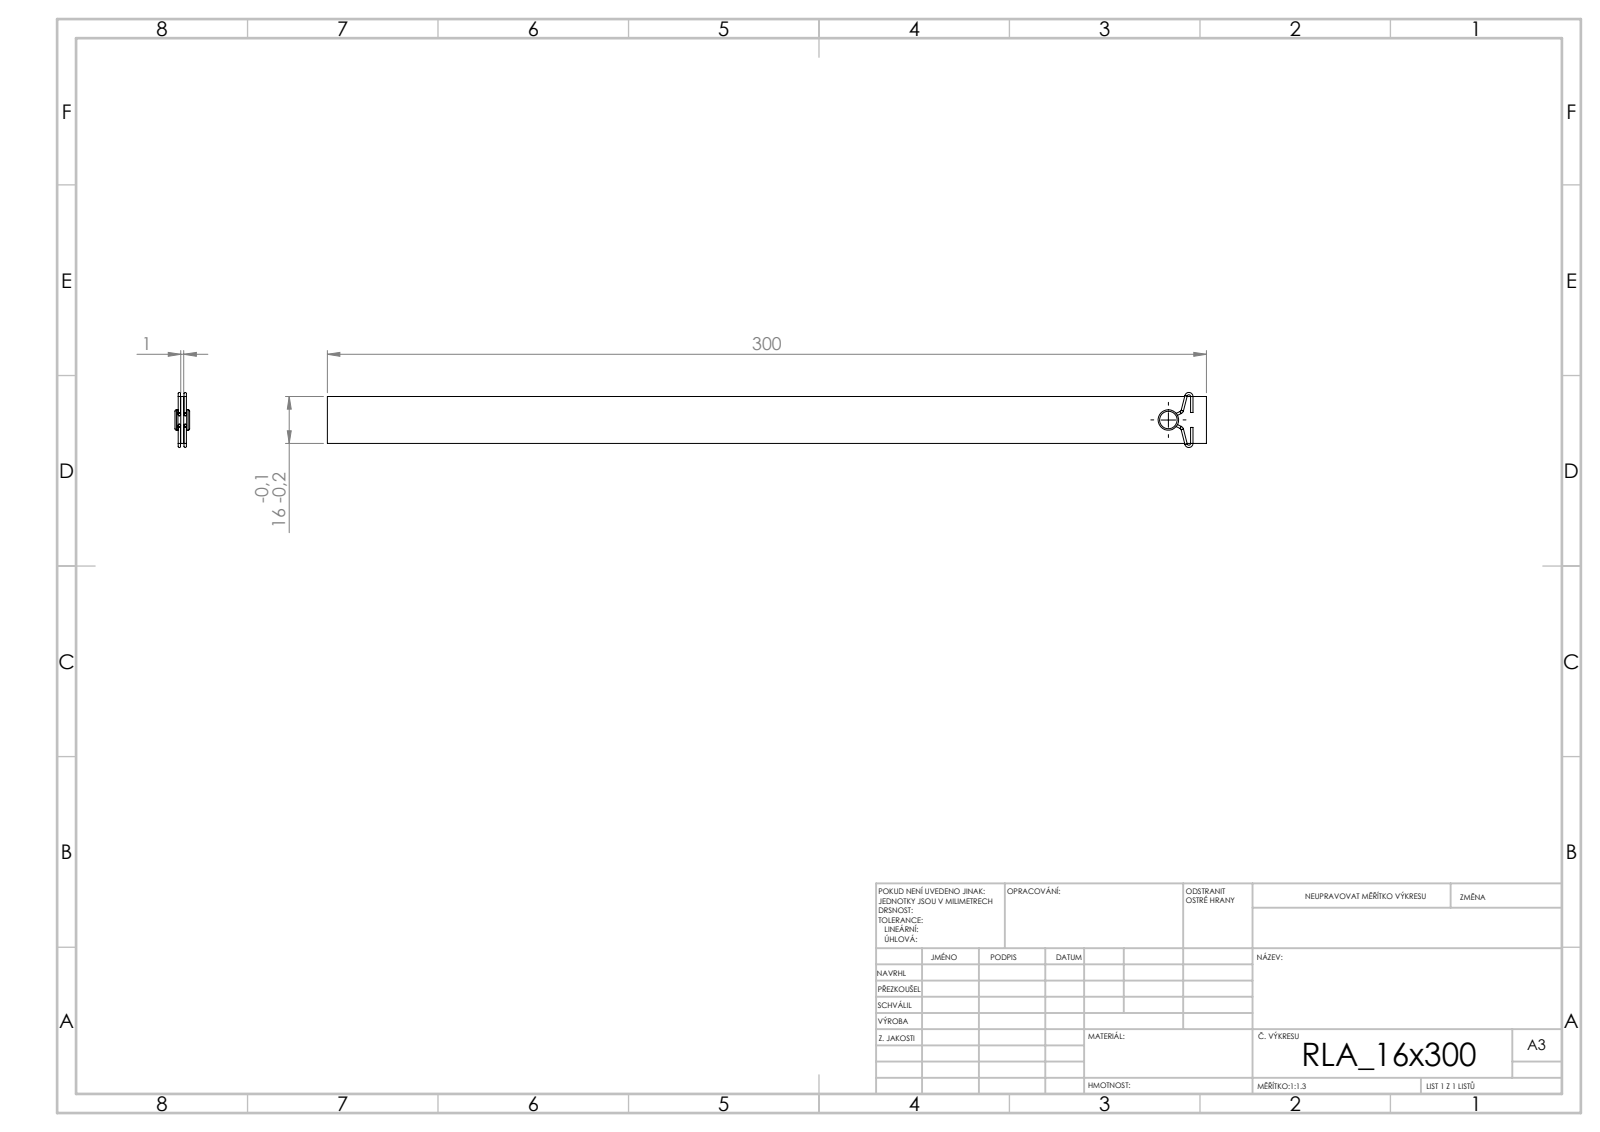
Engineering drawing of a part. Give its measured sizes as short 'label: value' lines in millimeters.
written by: SolidWorks 2019 (CONFIG_CONTROL_DESIGN)
unit: mm
bodies: 3 solids, 82 faces (14 planar, 40 cylindrical, 28 other)
size: 300 × 18.8 × 5
volume: 4 946 mm³; area: 10 627 mm²
bosses: 14× ⌀0.8, 1× ⌀7, 1× ⌀4
face distances: 1, 16, 2, 3, 4, 5, 300, 5.45, 10.55, 5.1
